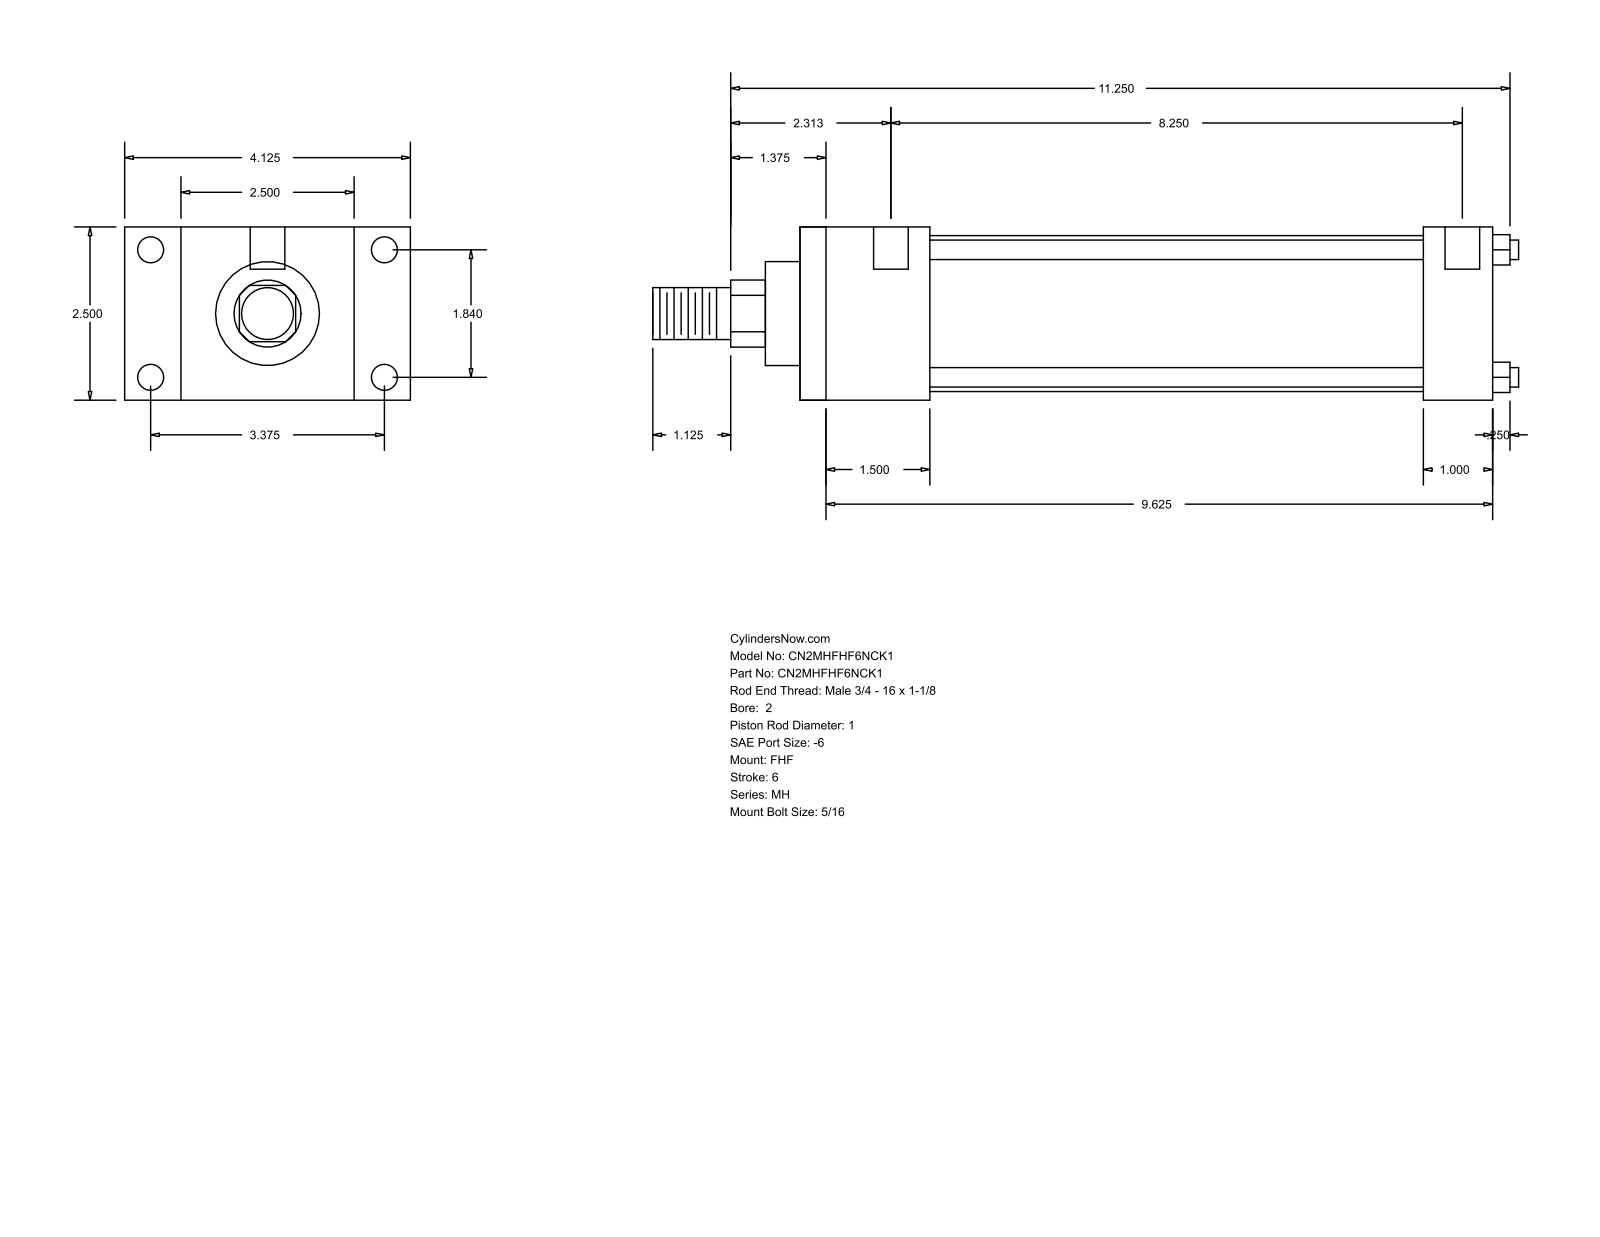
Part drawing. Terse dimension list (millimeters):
name: MH_FHF__0200_1
written by: GSSL Pune (CONFIG_CONTROL_DESIGN)
unit: mm
bodies: 0 solids, 88 faces (60 planar, 28 cylindrical, 0 other)
size: 317.5 × 104.78 × 63.5
holes: 4× ⌀5.56, 4× ⌀9.53, 2× ⌀12.7
bosses: 4× ⌀7.14, 1× ⌀57.15, 1× ⌀38.1, 1× ⌀25.4, 1× ⌀19.05
rounds: 1× R12.29
face distances: 63.5, 254, 47.63, 206.37, 20.64, 84.14, 104.78, 25.4, 228.6, 180.97
hole spacings: 46.74, 85.72, 97.63, 217.48, 3.17, 4.76, 209.55, 212.72
